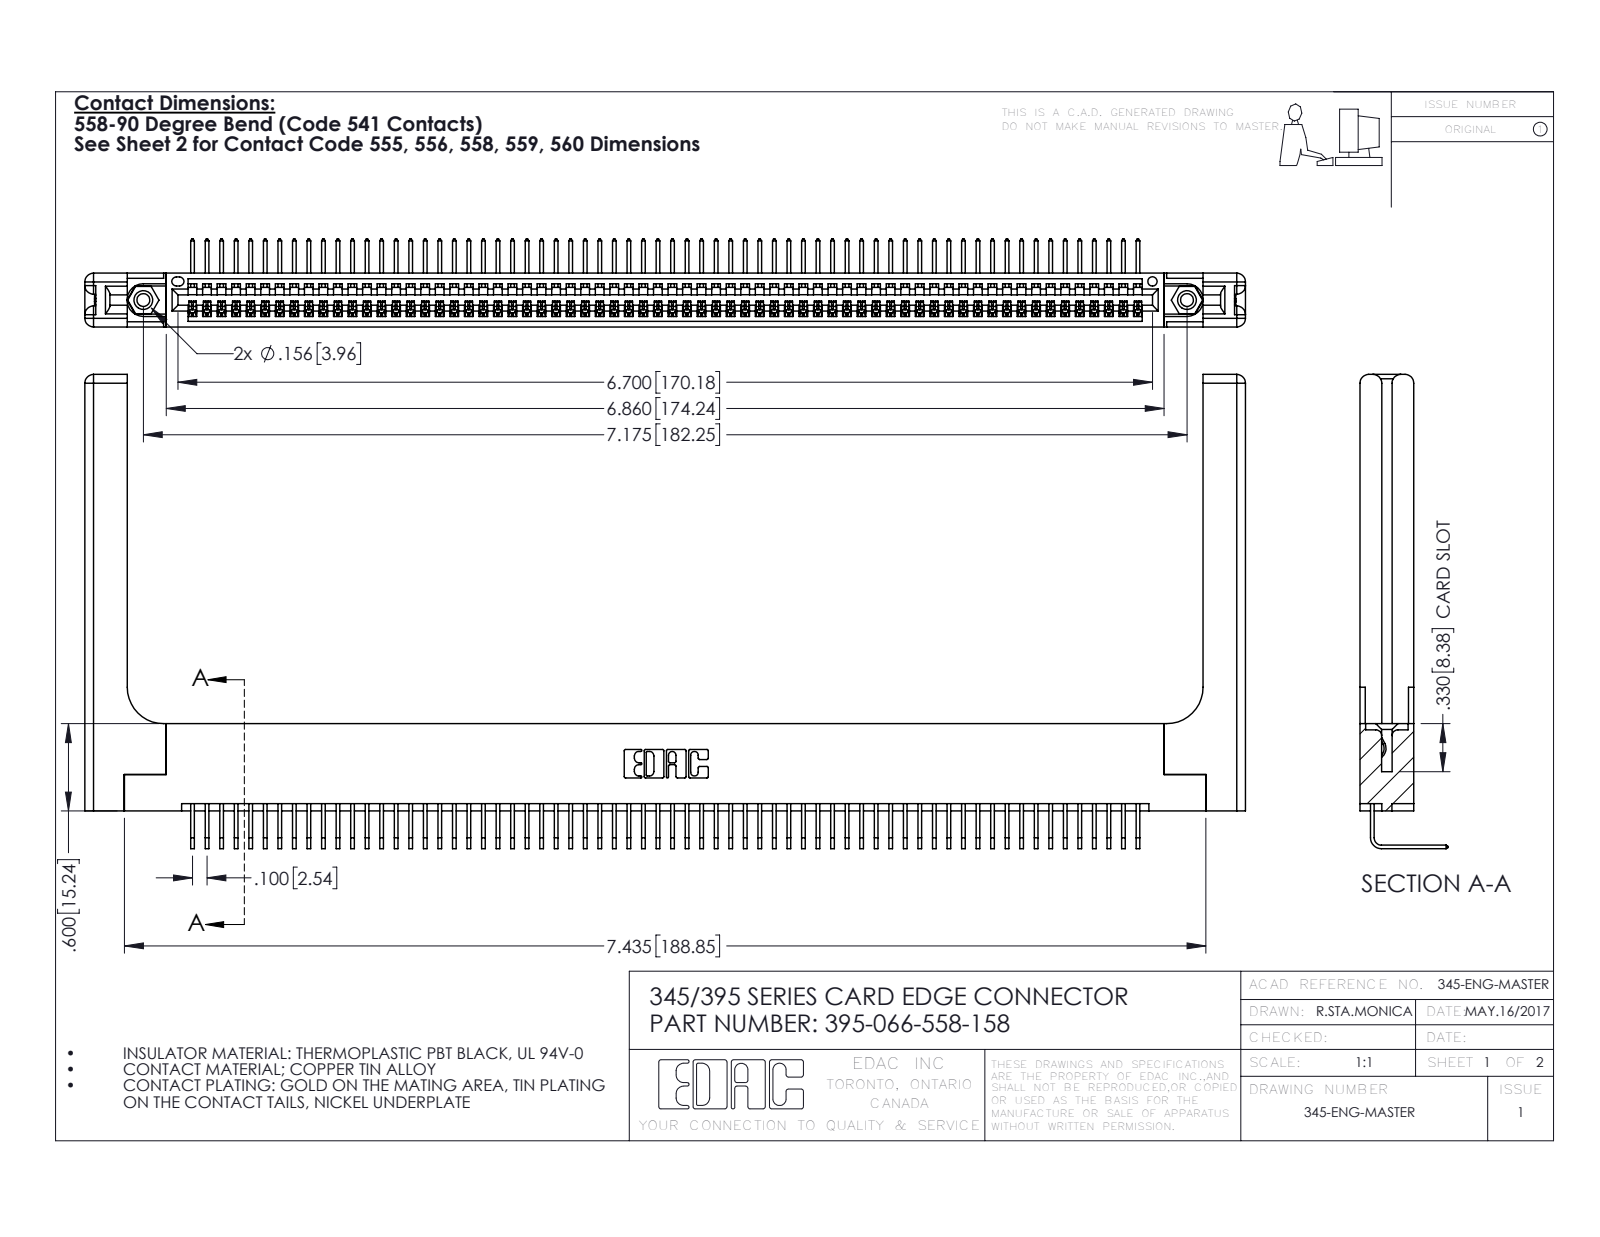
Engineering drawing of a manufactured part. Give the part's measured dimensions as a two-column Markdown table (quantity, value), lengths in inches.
| quantity | value |
| --- | --- |
| part name | 345 Part_Flush Mounting Lugs - 0.156 Dia-TH; 345-220-058_345-220-058; 345-292-001_558 Tail - 2; 395-066-558-158 (+1 more) |
| STEP written by | SolidWorks 2016 (CONFIG_CONTROL_DESIGN) |
| units | inches |
| bodies | 71 solids, 4342 faces (3000 planar, 1282 cylindrical, 60 other) |
| overall size | 7.979 × 3.259 × 0.605 |
| volume | 1.719 in³ |
| surface area | 51.24 in² |
| round holes (diameter × count) | 0.089 × 2, 0.125 × 2, 0.156 × 2, 0.064 × 1 |
| round bosses / shafts (diameter × count) | 0.155 × 2 |
| partial cylindrical surfaces (radius × count) | 0.006 × 132, 0.01 × 22, 0.06 × 16, 0.007 × 6, 0.031 × 6, 0.026 × 3, 0.03 × 2, 0.031 × 2 |
| main face-to-face distances | 0.072, 0.298, 0.37, 0.2, 0.098, 0.272, 0.025, 0.225, 0.148, 0.15 |
| hole center spacings | 0.27, 6.939, 7.175 |
